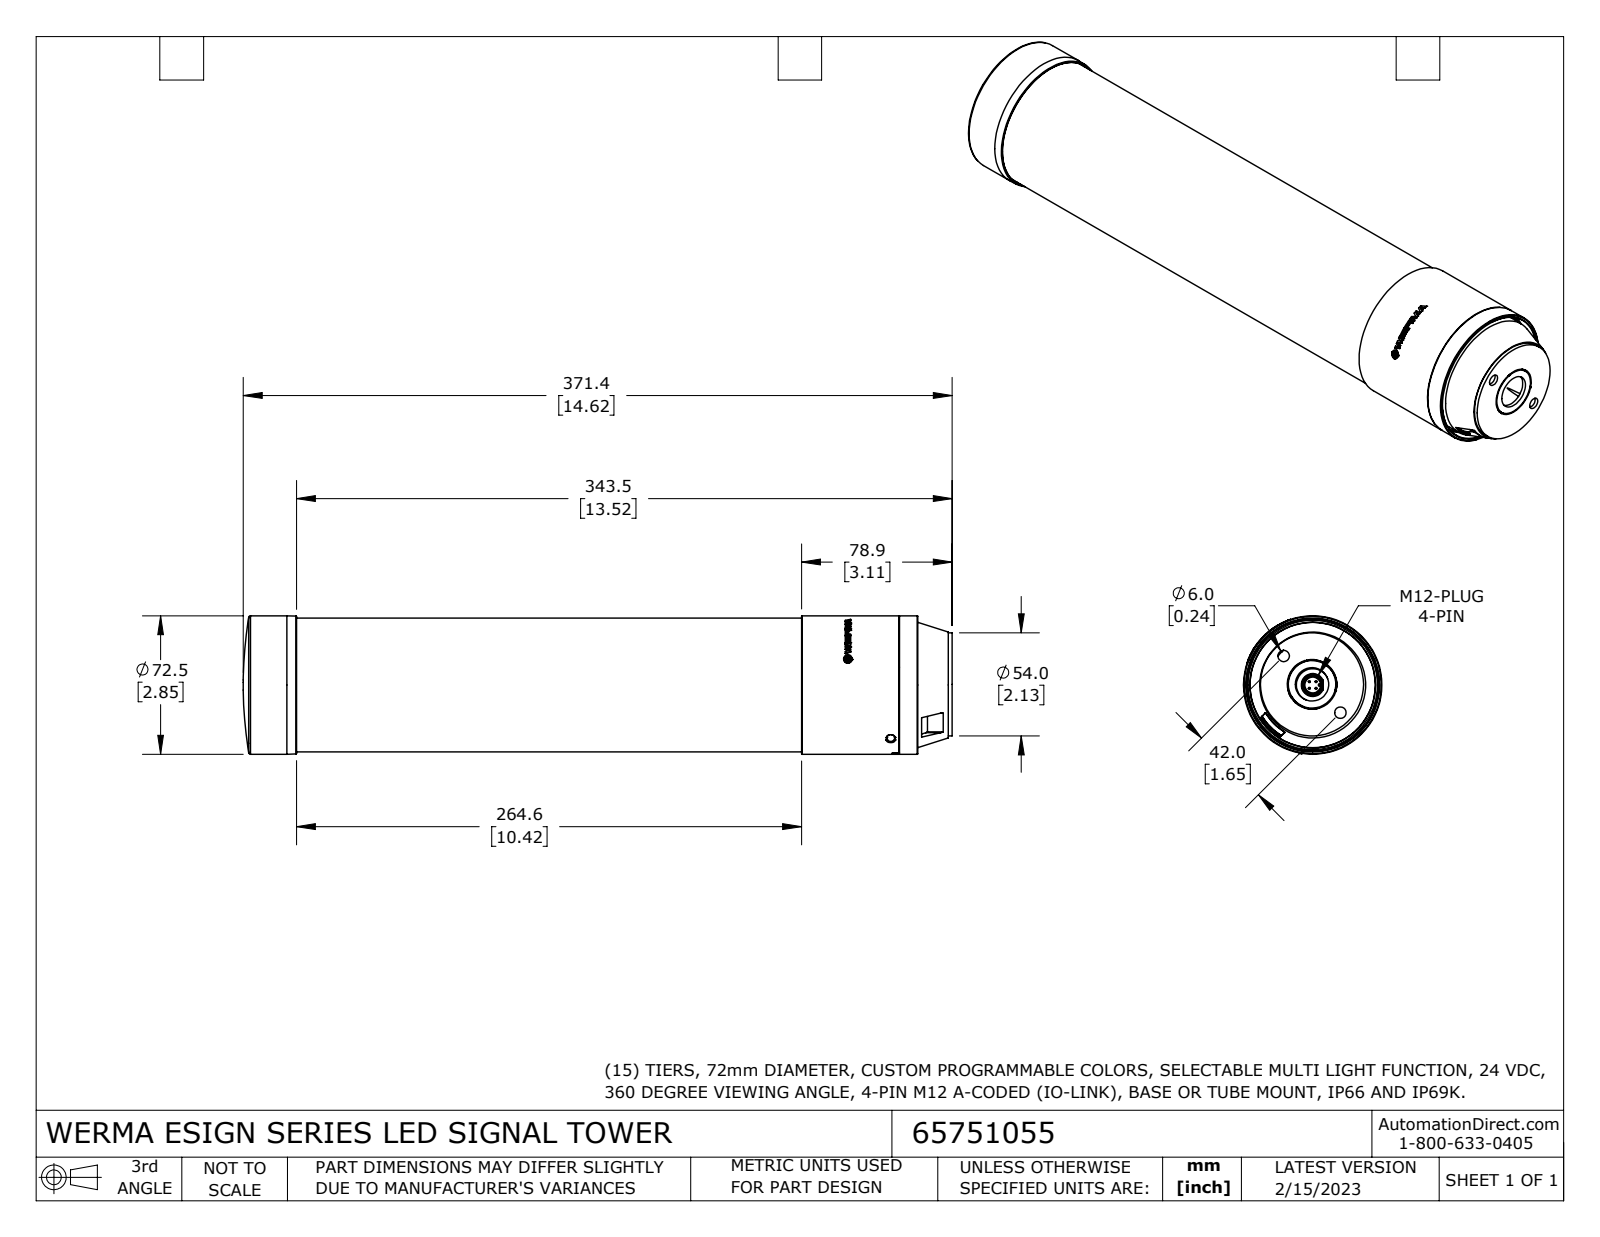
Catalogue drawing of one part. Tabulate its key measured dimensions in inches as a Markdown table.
| quantity | value |
| --- | --- |
| part name | 65751055 |
| STEP written by | SolidWorks 2021 (CONFIG_CONTROL_DESIGN) |
| units | inches |
| bodies | 1 solid, 395 faces (139 planar, 107 cylindrical, 149 other) |
| overall size | 14.621 × 2.854 × 2.854 |
| volume | 86.2 in³ |
| surface area | 154.4 in² |
| round holes (diameter × count) | 0.236 × 2, 0.327 × 1, 0.689 × 1, 1.024 × 1 |
| round bosses / shafts (diameter × count) | 0.039 × 4, 2.854 × 1, 2.756 × 1, 2.126 × 1, 0.98 × 1, 0.472 × 1, 0.413 × 1, 0.173 × 1 |
| partial cylindrical surfaces (radius × count) | 0.01 × 12, 0.012 × 12, 0.079 × 2, 0.08 × 2, 0.099 × 2, 0.009 × 1, 0.011 × 1, 0.016 × 1 |
| main face-to-face distances | 0.079, 2.909, 1.004, 0.925, 2.988, 1.984, 0.63, 0.709, 0.295, 2.28 |
| hole center spacings | 0.827, 0.019, 0.807, 0.846, 1.654 |
